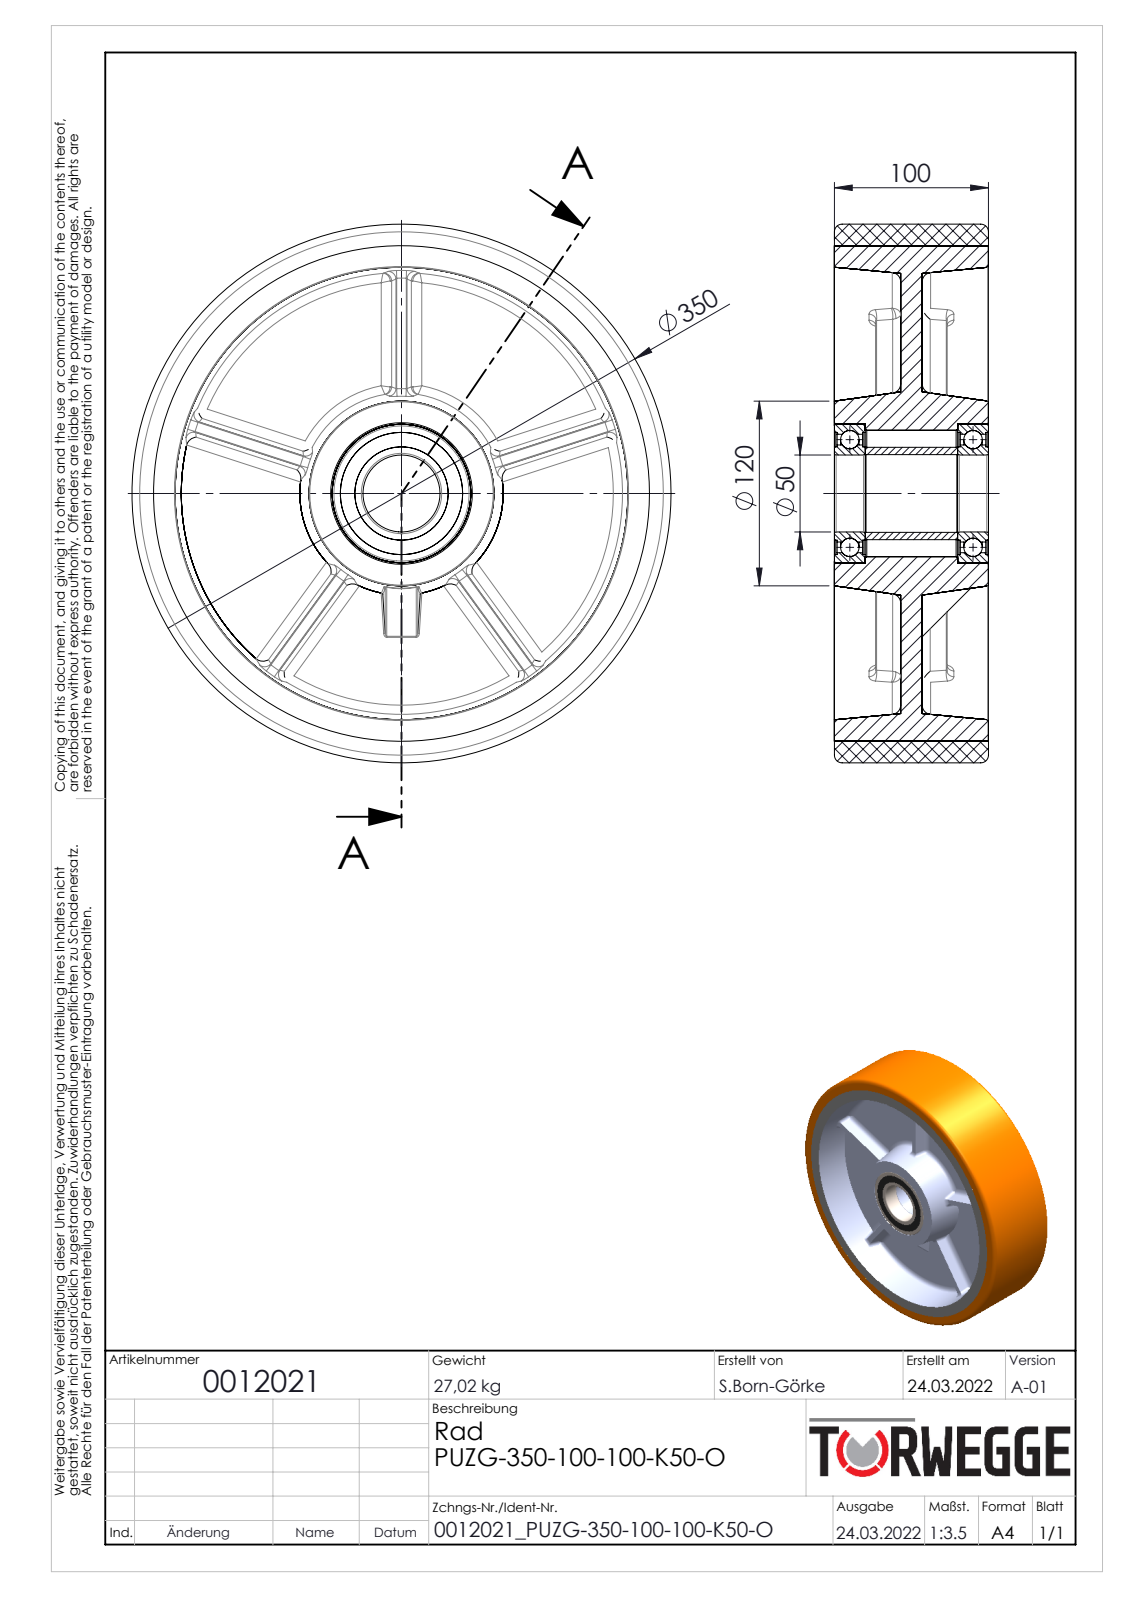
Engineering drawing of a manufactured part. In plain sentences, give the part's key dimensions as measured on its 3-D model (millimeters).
The part is named "0012021". Its 3-D file was written by "SolidWorks 2020 (AUTOMOTIVE_DESIGN)". It is 17 solids with 544 faces: 121 planar, 149 cylindrical and 274 other. Overall it measures 350 by 350 by 100.02 millimeters. Its volume is 16 720 000 cubic millimeters and its surface area 2 261 000 square millimeters. Round holes: 1 of diameter 50, 1 of diameter 50.5, 1 of diameter 60.6, 1 of diameter 76.96, 1 of diameter 79.4, 1 of diameter 82, 1 of diameter 90. Round bosses or shafts: 1 of diameter 350, 1 of diameter 322, 1 of diameter 63.04, 1 of diameter 60. Partial cylindrical surfaces (rounded edges, fillets, slot ends): 20 of radius 0.5, 20 of radius 7, 5 of radius 1. The main face-to-face distances are 14, 43, 57, 100, 80, 20, 23, 37, 20.01, 43.01.
